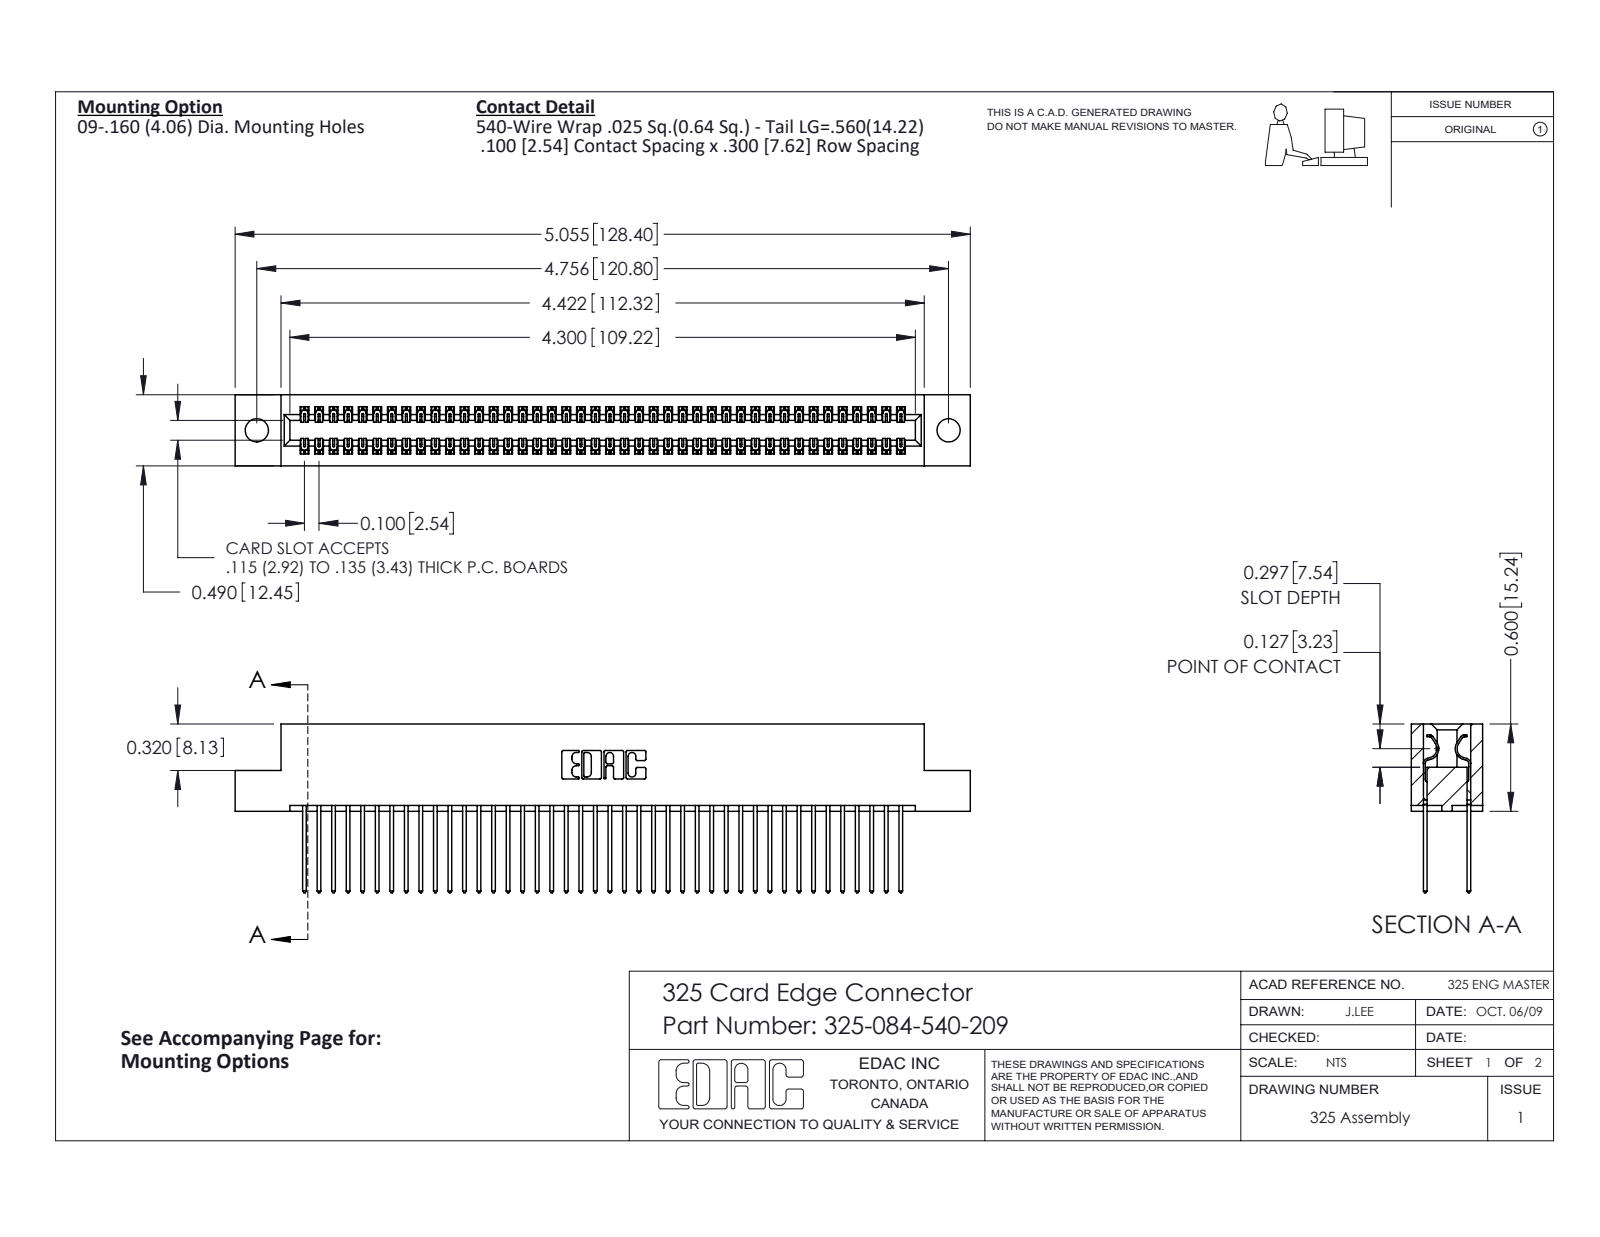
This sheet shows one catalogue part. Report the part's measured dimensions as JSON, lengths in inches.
{"part_name": "325 Part_.160 TH; 325-084-540-209; 325-292-001_325-293-140", "step_written_by": "SolidWorks 2016 (CONFIG_CONTROL_DESIGN)", "units": "inches", "bodies": {"solids": 85, "faces": 4482, "planar": 3094, "cylindrical": 1388, "other": 0}, "overall_size": [5.055, 1.16, 0.49], "volume_in3": 1.017, "surface_area_in2": 33.49, "round_holes": [[0.16, 2]], "partial_cylinders_radius": [[0.006, 126], [0.01, 84], [0.01, 22], [0.007, 6], [0.031, 6], [0.026, 3], [0.014, 2], [0.022, 2]], "face_to_face_distances": [0.083, 0.407, 0.3, 0.107, 0.383, 0.025, 0.325, 0.49, 0.275, 0.56], "hole_center_spacings": [4.756]}
